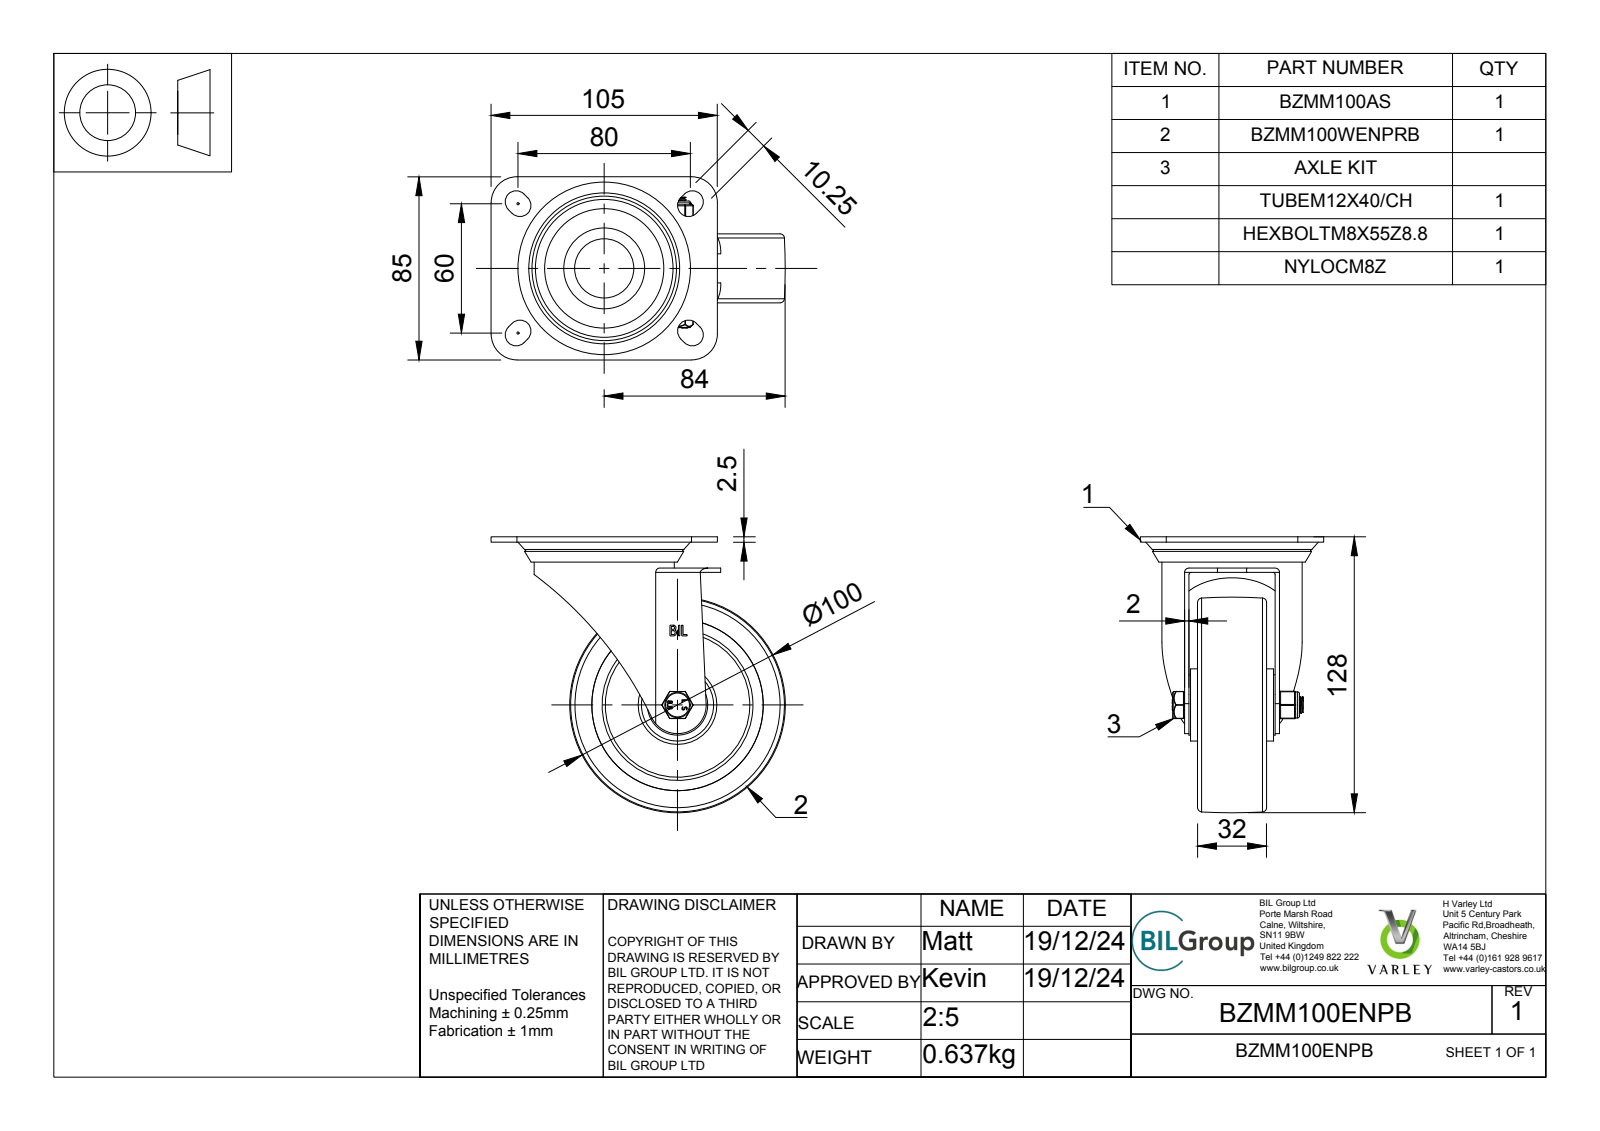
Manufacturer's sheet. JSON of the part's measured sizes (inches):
{"part_name": "BZMM100ENPB v3; BZMM100AS - 2 v2; ZINC PLATED, PRESSED STEEL TOP PLATE; ZINC PLATED, PRESSED STEEL TOP PLATE Geometry (+7 more)", "step_written_by": "Autodesk Translation Framework v13.20.0.188 (AP242_MANAGED_MODEL_BASED_3D_ENGINEERING_MIM_LF)", "units": "inches", "bodies": {"solids": 43, "faces": 478, "planar": 193, "cylindrical": 169, "other": 116}, "overall_size": [5.374, 5.039, 3.346], "volume_in3": 13.83, "surface_area_in2": 182.2, "round_holes": [[0.026, 2], [0.315, 1], [0.325, 1], [0.331, 1], [0.339, 1], [0.492, 1], [0.512, 1], [0.787, 1], [0.87, 1], [1.083, 1], [1.89, 1], [2.402, 1]], "round_bosses_or_shafts": [[0.157, 8], [2.559, 1], [1.319, 1], [1.24, 1], [1.102, 1], [0.866, 1], [0.768, 1], [0.476, 1]], "partial_cylinders_radius": [[0.02, 18], [0.01, 12], [0.202, 8], [0.013, 4], [0.025, 4], [0.039, 4], [0.472, 4], [0.025, 2]], "face_to_face_distances": [0.709, 0.157, 0.079, 0.551, 0.098, 0.866, 1.417, 0.787, 1.496, 1.26], "hole_center_spacings": [0.127, 0.098]}
